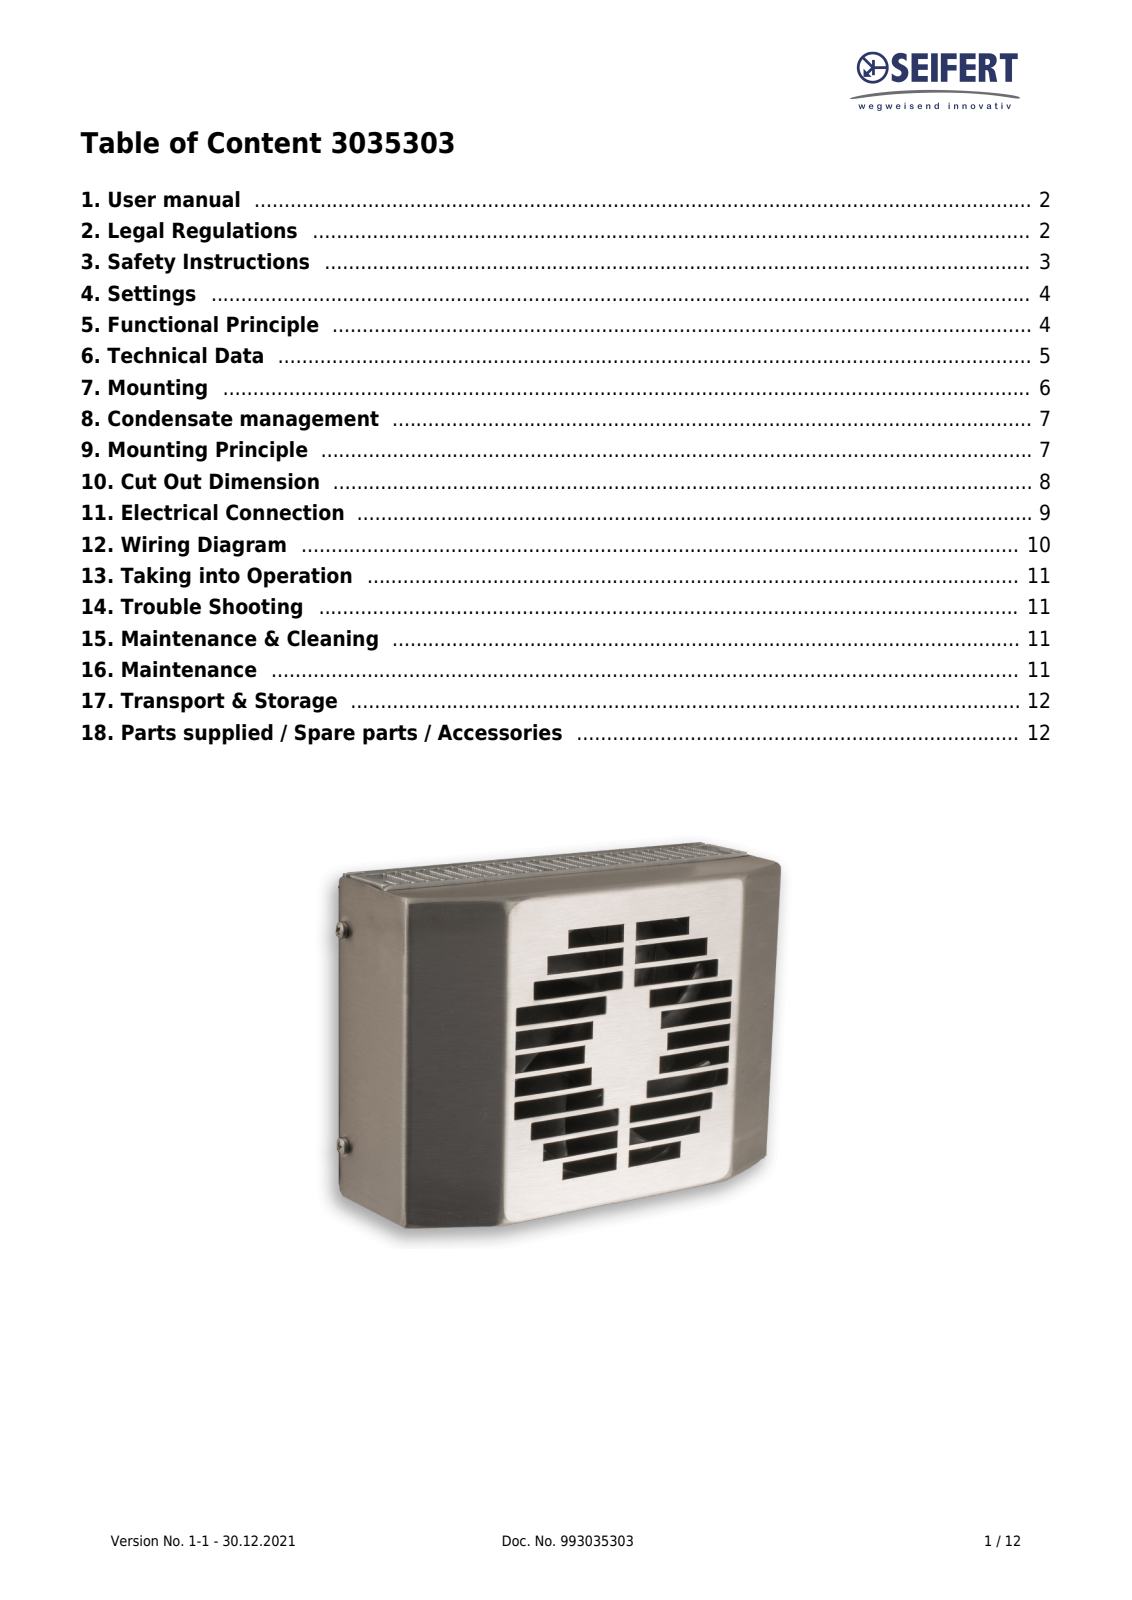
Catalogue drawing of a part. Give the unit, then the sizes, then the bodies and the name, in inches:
Units: inches
Overall size (bounding box): 6.23 × 5.258 × 4.331
Round holes (diameter × count): ⌀0.177 ×12, ⌀0.165 ×10, ⌀0.236 ×8, ⌀0.315 ×5, ⌀0.138 ×4, ⌀0.169 ×4, ⌀0.197 ×4, ⌀0.098 ×2, ⌀0.126 ×2, ⌀0.244 ×2, ⌀0.295 ×1, ⌀0.394 ×1
Round bosses / shafts (diameter × count): ⌀0.071 ×12, ⌀0.154 ×4, ⌀0.094 ×4, ⌀0.236 ×2, ⌀0.118 ×2, ⌀0.097 ×2, ⌀1.969 ×1
Partial cylindrical surfaces — rounded edges, fillets, slot ends (radius × count): R0.029 ×998, R0.031 ×143, R0.005 ×16, R0.079 ×10, R0.039 ×8, R0.167 ×4, R0.087 ×3, R0.118 ×2
Main face-to-face distances: 0.039, 0.118, 0.197, 0.079, 0.65, 0.217, 1.181, 2.801, 0.433, 1.299
Hole centre spacings: 2.924, 0.1, 0.278, 0.328, 1.102, 1.152, 1.202, 1.245
Volume: 38 in³ · Surface area: 723.7 in²
Bodies: 23 solids, 3130 faces (1450 planar, 1512 cylindrical, 168 other)
Part name (STEP PRODUCT): tg3035
STEP written by: SolidWorks 2021 (AUTOMOTIVE_DESIGN)
